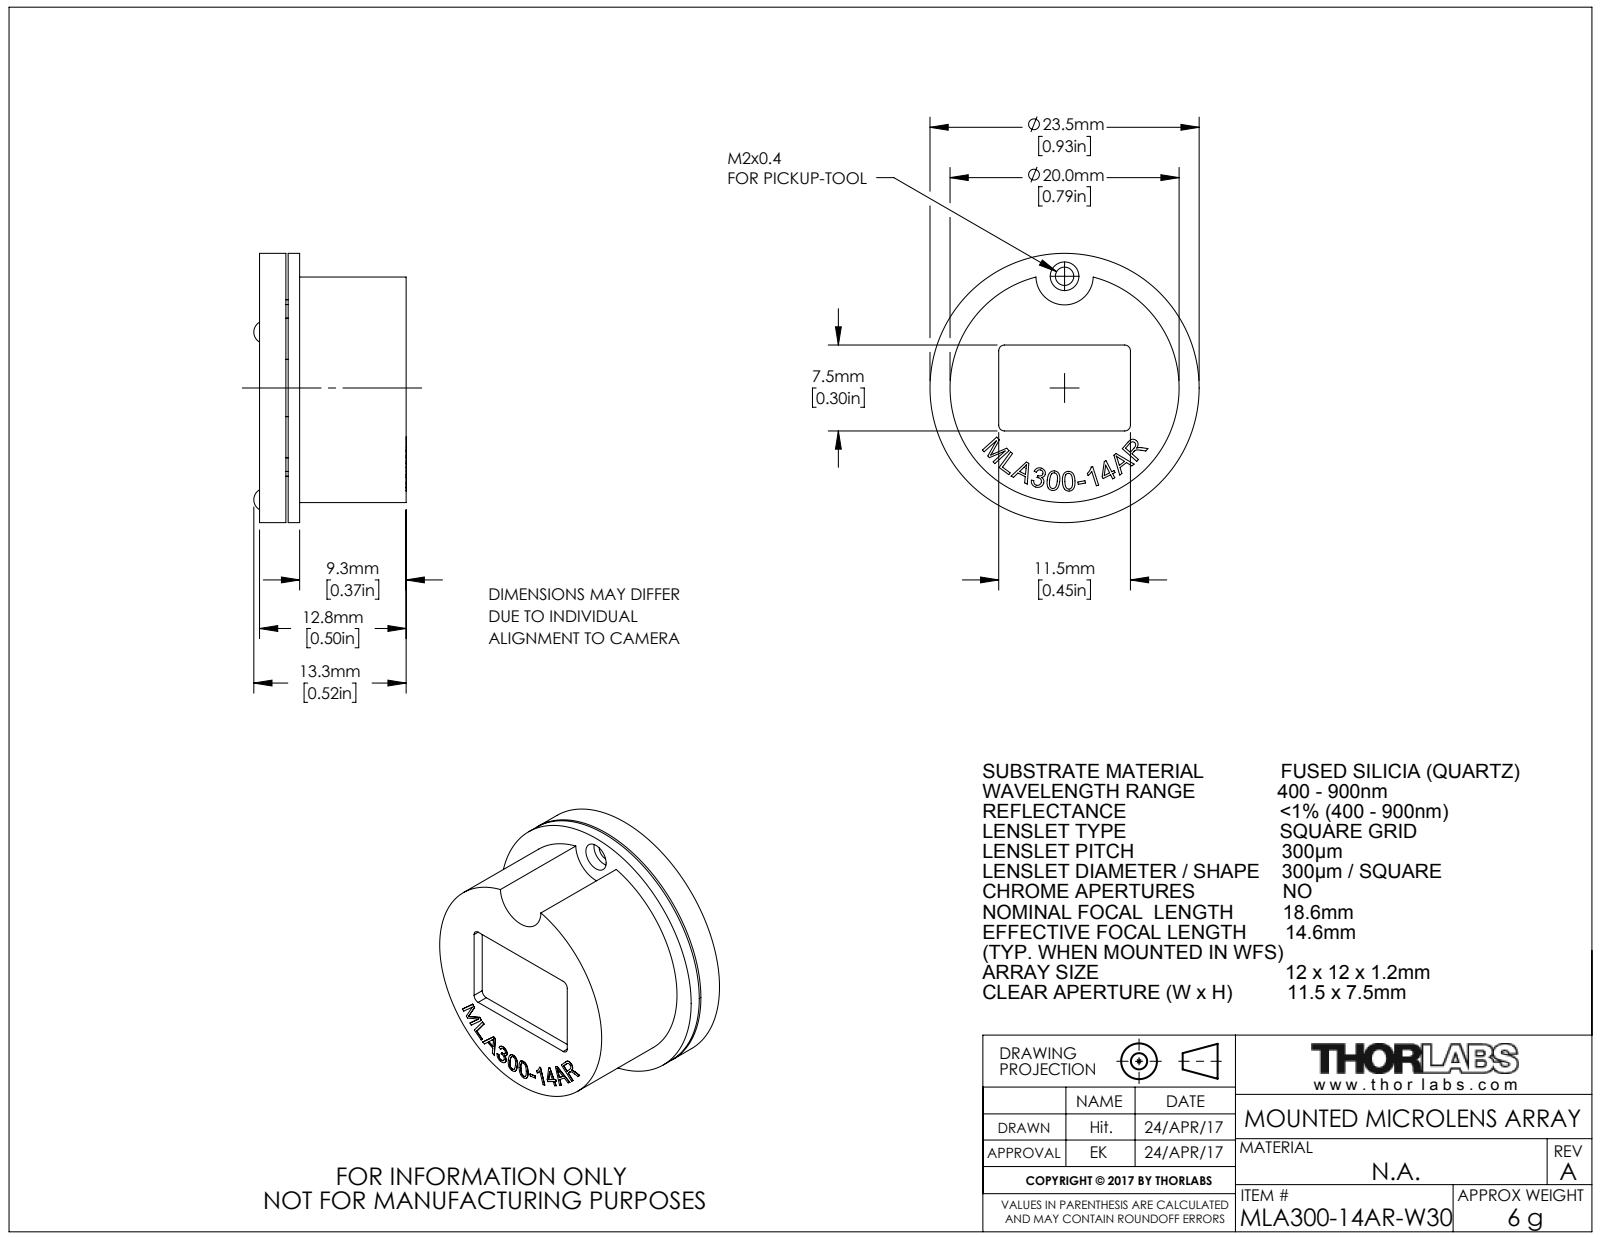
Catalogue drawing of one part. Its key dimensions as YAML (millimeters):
part_name: "MTN009304-E0W"
step_written_by: "SolidWorks 2016 (AUTOMOTIVE_DESIGN)"
units: millimeters
bodies: {solids: 12, faces: 295, planar: 169, cylindrical: 70, other: 56}
overall_size: [23.5, 23.5, 13.31]
volume: 2329
surface_area: 3367
round_holes:
  - {diameter: 3.2, count: 6}
  - {diameter: 1.9, count: 3}
  - {diameter: 1.5, count: 1}
  - {diameter: 1.6, count: 1}
  - {diameter: 2.5, count: 1}
round_bosses_or_shafts:
  - {diameter: 3, count: 6}
  - {diameter: 23.5, count: 1}
  - {diameter: 20, count: 1}
partial_cylinders:
  - {radius: 0.5, count: 8}
  - {radius: 2.5, count: 5}
  - {radius: 7.7, count: 1}
  - {radius: 7.75, count: 1}
face_to_face_distances: [1, 1.2, 9.3, 9.5, 8.3, 10.5, 10.3, 2.2, 12.8, 11.8]
hole_center_spacings: [18.83, 13.79, 16.88, 5.04, 5.05, 9.74, 16.89, 9.75]
